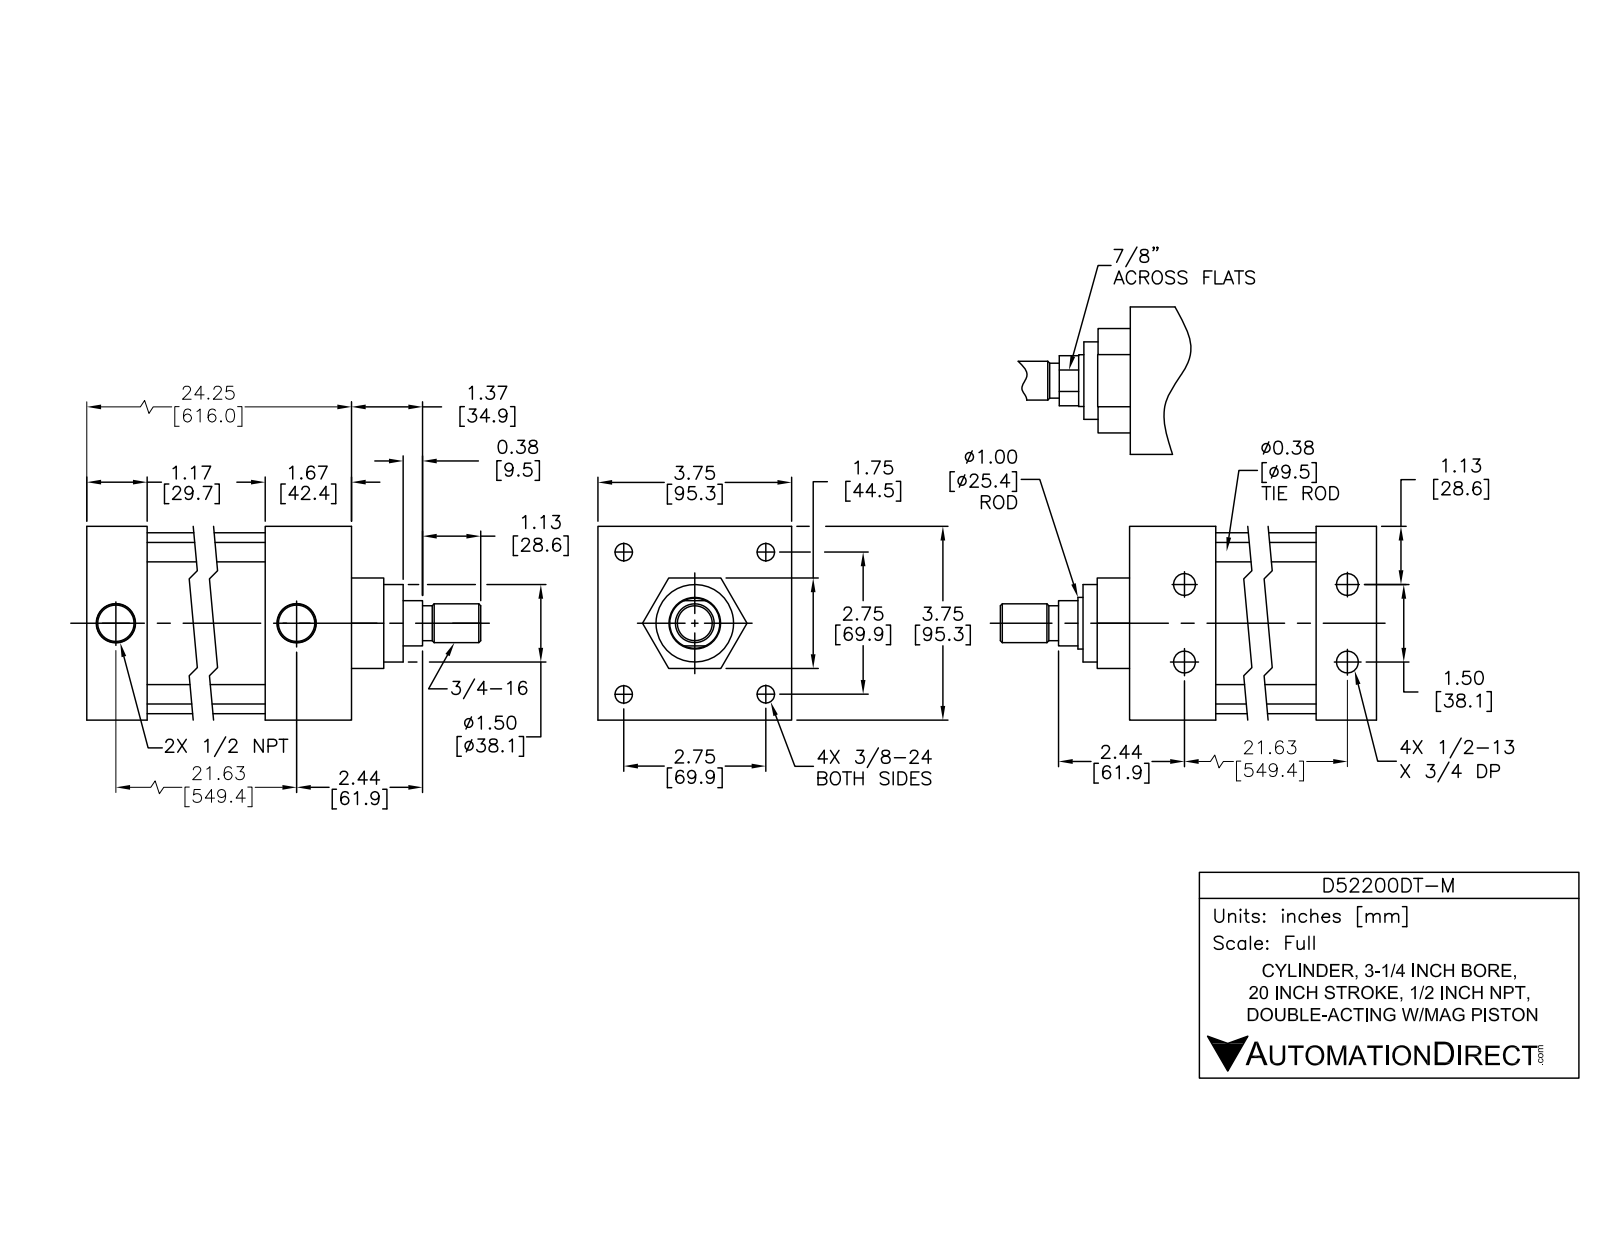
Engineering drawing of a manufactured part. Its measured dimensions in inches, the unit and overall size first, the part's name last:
Units: inches
Overall size (bounding box): 26.745 × 3.75 × 3.75
Round holes (diameter × count): ⌀0.33 ×4, ⌀0.406 ×4, ⌀0.417 ×4, ⌀0.625 ×4, ⌀0.5 ×2, ⌀0.766 ×2, ⌀1 ×1, ⌀1.003 ×1, ⌀3.25 ×1
Round bosses / shafts (diameter × count): ⌀0.609 ×4, ⌀0.375 ×4, ⌀0.34 ×4, ⌀3.5 ×1, ⌀3.247 ×1, ⌀1.75 ×1, ⌀0.997 ×1, ⌀0.97 ×1
Partial cylindrical surfaces — rounded edges, fillets, slot ends (radius × count): R0.375 ×4
Main face-to-face distances: 3.75, 0.08, 21.326, 24.246, 1.75, 22.997, 1.249, 21.751, 1.246, 2.495
Hole centre spacings: 1.95, 2.758, 0.75, 0.76, 1.5, 3.901, 22.5, 22.517
Volume: 103.2 in³ · Surface area: 809.3 in²
Bodies: 12 solids, 303 faces (99 planar, 114 cylindrical, 90 other)
Part name (STEP PRODUCT): D52200DT-M PISTON; D52200DT-M BODY; D52200DT-M
STEP written by: SolidWorks 2015 (AUTOMOTIVE_DESIGN)
